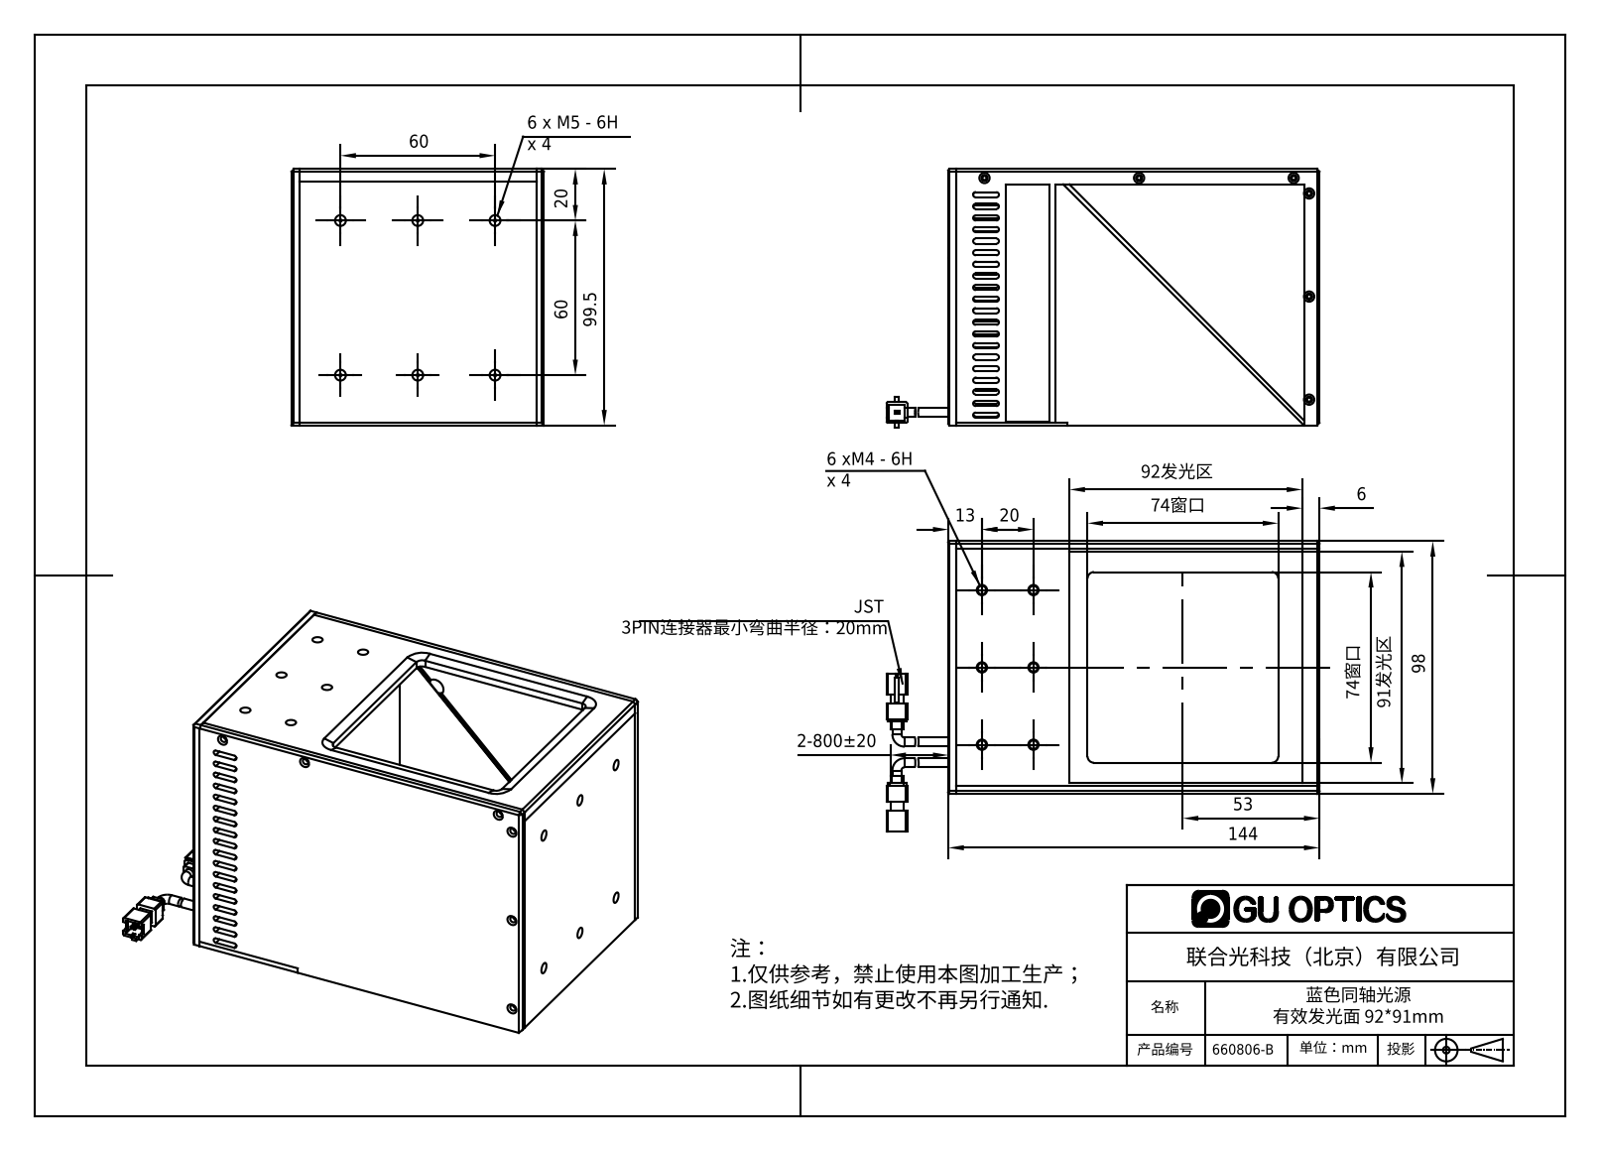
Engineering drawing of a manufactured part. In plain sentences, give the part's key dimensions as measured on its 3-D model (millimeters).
The part is named "蓝色同轴光源 有效发光面 9291mm". Its 3-D file was written by "SolidWorks 2016 (AUTOMOTIVE_DESIGN)". It is 22 solids with 4262 faces: 906 planar, 2251 cylindrical and 1105 other. Overall it measures 168 by 110.5 by 99.7 millimeters. Its volume is 274 829 cubic millimeters and its surface area 199 655 square millimeters. Round holes: 16 of diameter 1.6, 16 of diameter 2.4, 14 of diameter 2, 6 of diameter 3.3, 6 of diameter 4, 6 of diameter 4.2, 4 of diameter 2.5, 4 of diameter 7, 2 of diameter 1, 2 of diameter 6.8, 1 of diameter 38, 1 of diameter 48. Round bosses or shafts: 462 of diameter 3.8, 462 of diameter 3, 3 of diameter 3.5, 1 of diameter 51, 1 of diameter 41. Partial cylindrical surfaces (rounded edges, fillets, slot ends): 76 of radius 1, 8 of radius 0.5, 8 of radius 1.76, 8 of radius 1.76, 8 of radius 1.77, 8 of radius 2, 4 of radius 2.5, 2 of radius 1.01. The main face-to-face distances are 4, 94, 2, 3, 98, 6, 90, 1, 141, 135. The hole center spacings are 30, 60, 50, 23.41, 35.36, 36.06, 67.08, 72.1.
